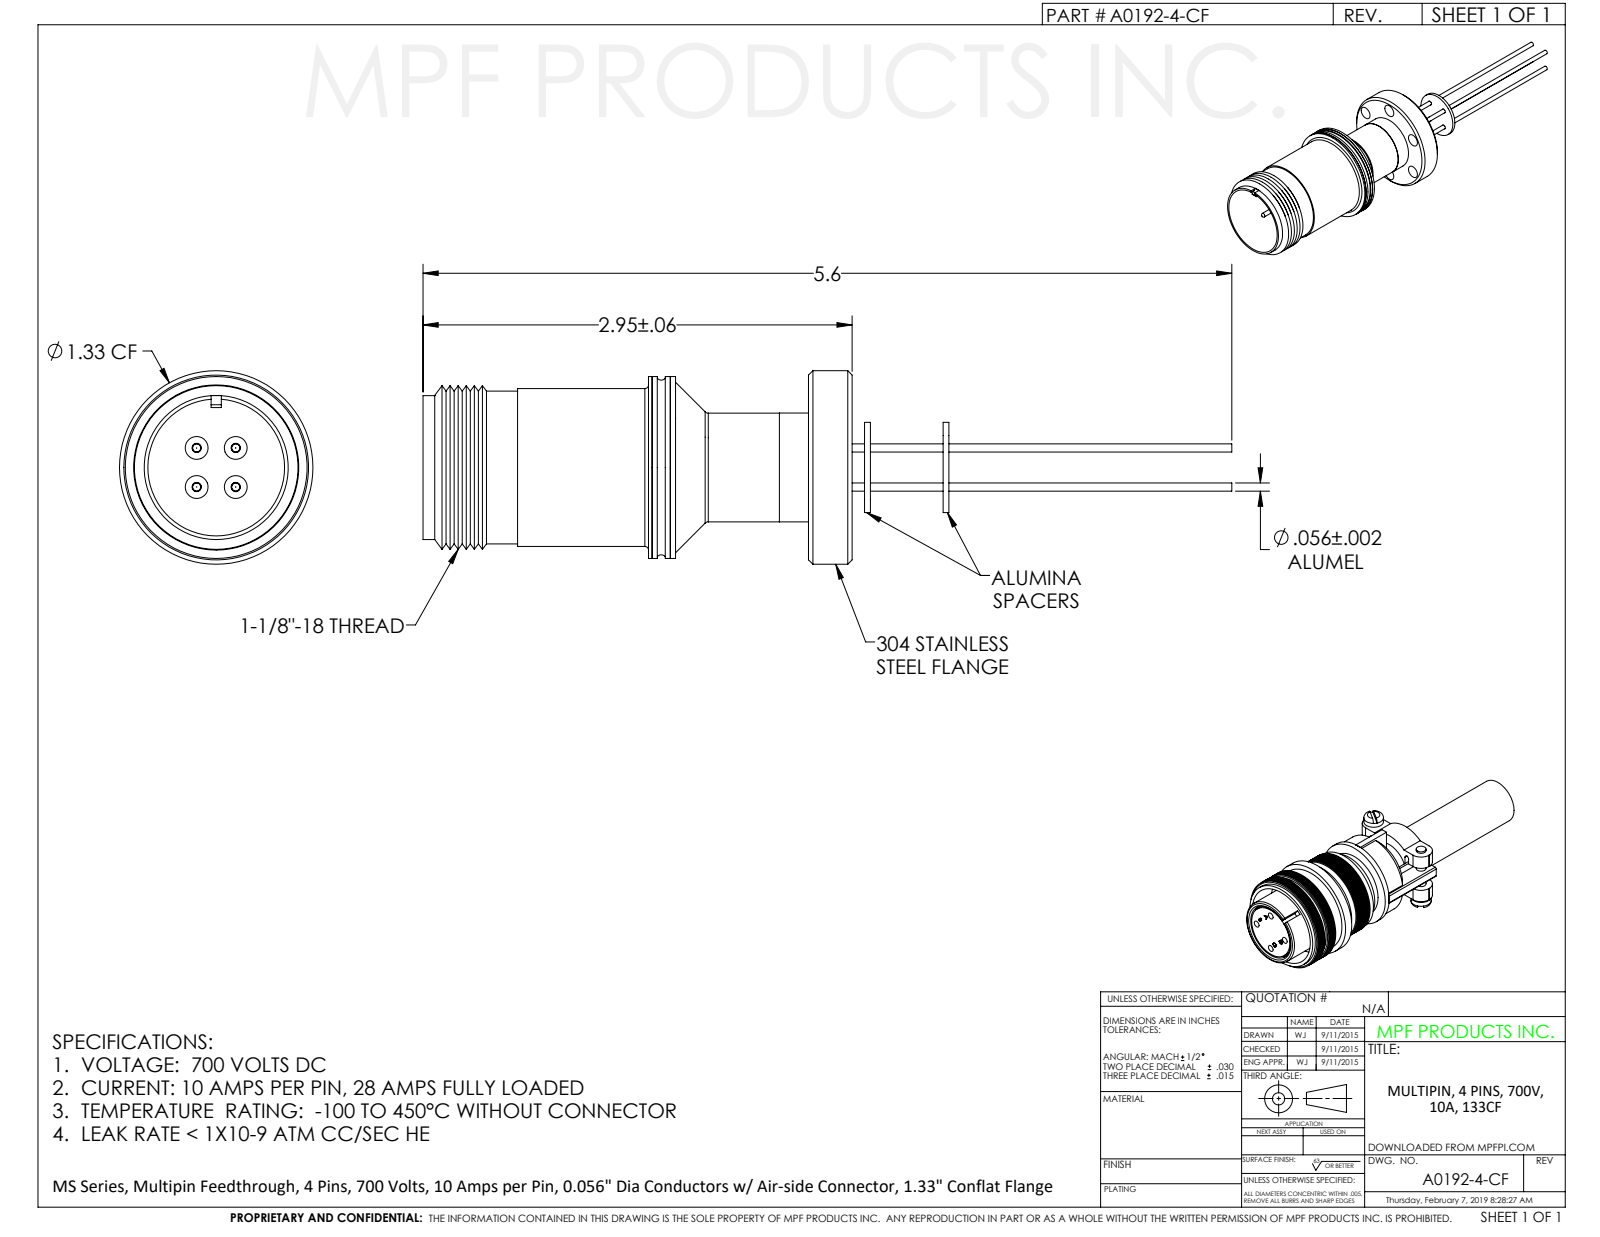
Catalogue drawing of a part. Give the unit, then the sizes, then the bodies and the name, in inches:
Units: inches
Overall size (bounding box): 5.595 × 1.33 × 1.33
Round holes (diameter × count): ⌀0.172 ×6, ⌀0.63 ×1, ⌀0.675 ×1, ⌀0.725 ×1, ⌀0.845 ×1, ⌀0.94 ×1, ⌀0.96 ×1, ⌀0.97 ×1, ⌀1.035 ×1
Round bosses / shafts (diameter × count): ⌀0.187 ×4, ⌀0.167 ×4, ⌀0.056 ×4, ⌀1.33 ×1, ⌀1.25 ×1, ⌀1.085 ×1, ⌀1.05 ×1, ⌀1.02 ×1
Main face-to-face distances: 1.52, 0.05, 1.47, 1.805, 1.755, 0.285, 0.04, 2.213, 0.15, 2.263
Hole centre spacings: 0.531, 0.92, 0.531, 1.062, 1.062
Volume: 0.892 in³ · Surface area: 32.66 in²
Bodies: 1 solid, 218 faces (54 planar, 110 cylindrical, 54 other)
Part name (STEP PRODUCT): A0192-4-CF
STEP written by: SolidWorks 2012 (CONFIG_CONTROL_DESIGN)
